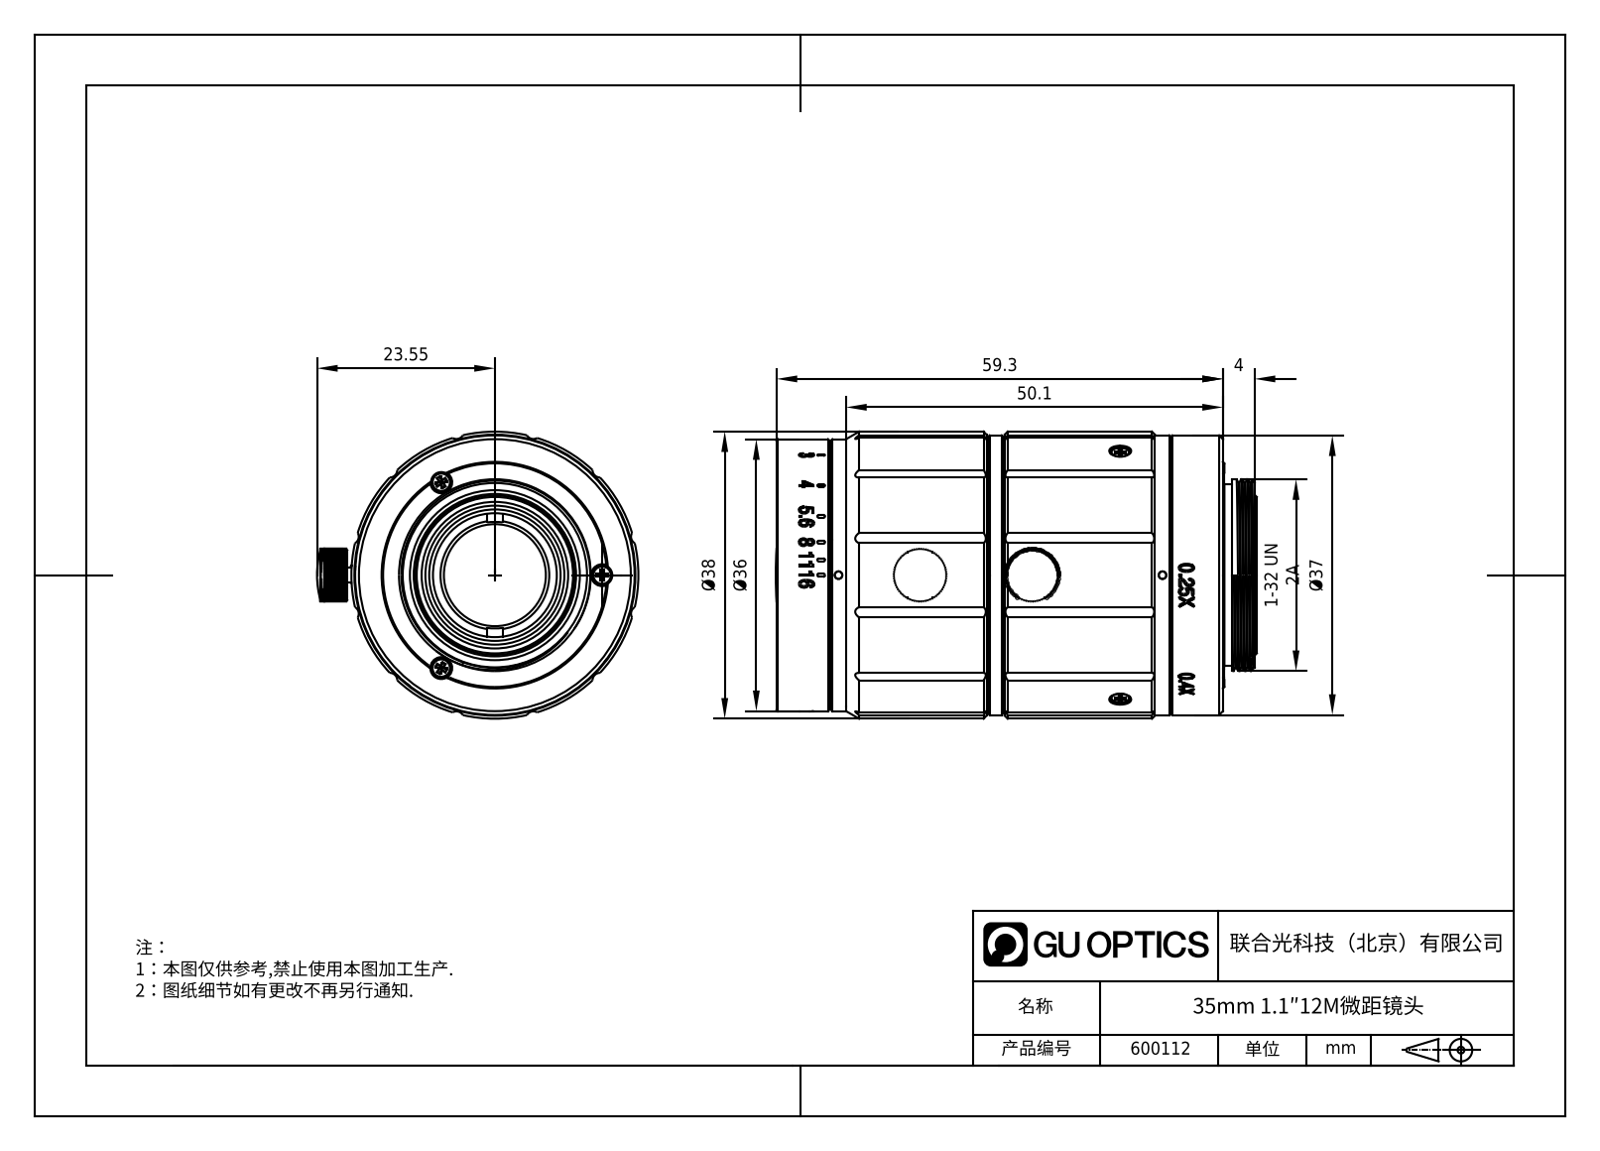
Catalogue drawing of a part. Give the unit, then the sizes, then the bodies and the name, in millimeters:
Units: millimetres
Overall size (bounding box): 63.69 × 42.55 × 38
Round holes (diameter × count): ⌀1.5 ×6, ⌀2 ×6, ⌀2.7 ×6, ⌀1 ×3, ⌀1.6 ×1, ⌀3.2 ×1, ⌀13.5 ×1, ⌀16 ×1, ⌀16.4 ×1, ⌀16.6 ×1, ⌀17.4 ×1, ⌀18 ×1
Round bosses / shafts (diameter × count): ⌀2.5 ×8, ⌀1.4 ×6, ⌀2.05 ×2, ⌀38 ×1, ⌀37 ×1, ⌀36 ×1, ⌀35.8 ×1, ⌀35.6 ×1
Partial cylindrical surfaces — rounded edges, fillets, slot ends (radius × count): R1 ×12, R3.4 ×2, R3.5 ×2, R12.27 ×1, R15 ×1, R17.95 ×1, R18.45 ×1
Main face-to-face distances: 54.5, 2, 3, 52.5, 24.5, 30.68, 21.82, 23.82, 28.6, 17.95
Hole centre spacings: 11.7, 14.2, 14.8, 24.6, 26.5, 6, 8.8, 20.5
Volume: 49 734 mm³ · Surface area: 42 028 mm²
Bodies: 21 solids, 1760 faces (703 planar, 510 cylindrical, 547 other)
Part name (STEP PRODUCT): 600112
STEP written by: SolidWorks 2020 (CONFIG_CONTROL_DESIGN)
